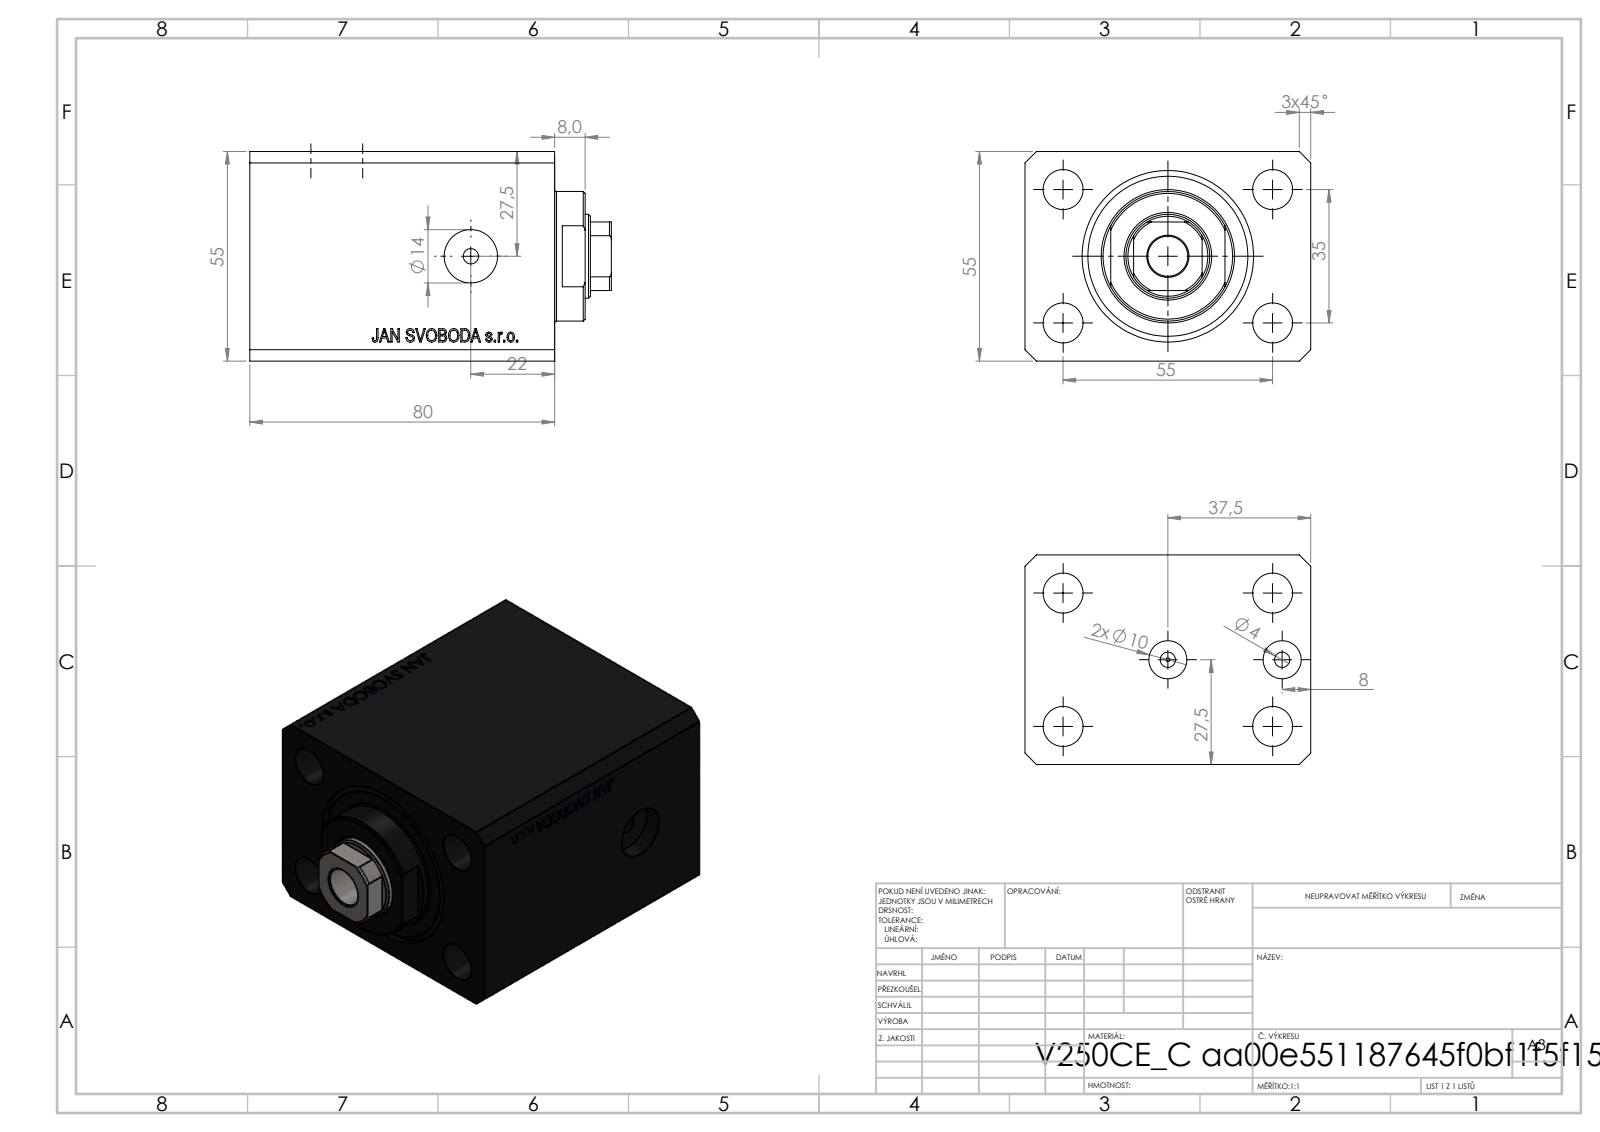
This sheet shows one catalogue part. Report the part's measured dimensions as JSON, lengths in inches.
{"part_name": "V250CE_C_Body; V250CE_C_VCP; V250CE_VC_C", "step_written_by": "SolidWorks 2019 (CONFIG_CONTROL_DESIGN)", "units": "inches", "bodies": {"solids": 3, "faces": 872, "planar": 428, "cylindrical": 50, "other": 394}, "overall_size": [3.736, 2.953, 2.165], "volume_in3": 18.08, "surface_area_in2": 104.2, "round_holes": [[0.413, 5], [0.157, 4], [0.394, 2], [0.551, 2], [0.049, 1], [0.866, 1], [1.26, 1], [1.772, 1]], "round_bosses_or_shafts": [[1.339, 1]], "partial_cylinders_radius": [[0.413, 1]], "face_to_face_distances": [2.165, 2.953, 3.15, 1.067, 2.083, 1.693, 0.39, 2.76, 3.451, 0.315], "hole_center_spacings": [1.283, 0.696, 1.378, 2.165, 2.366, 2.567, 1.181, 1.417]}
